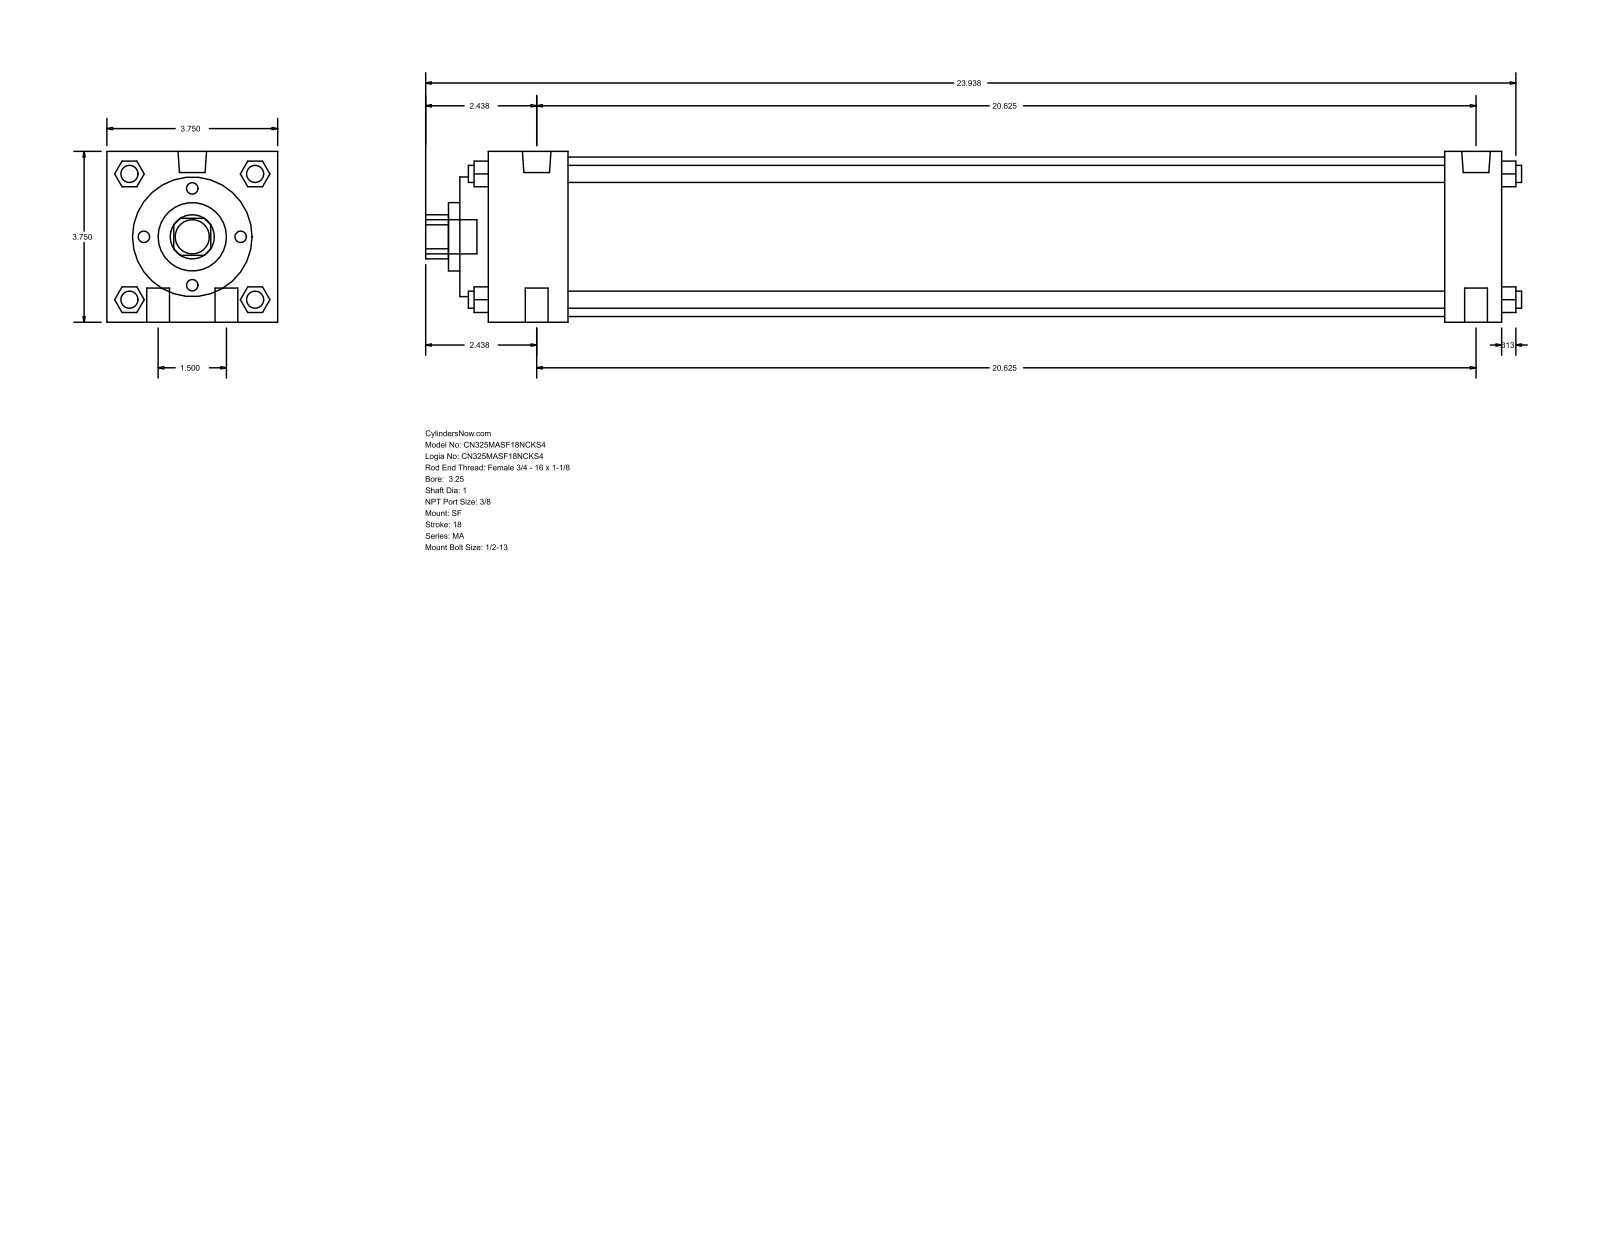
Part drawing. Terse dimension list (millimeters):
name: MA_SF__0325_1
written by: GSSL Pune (CONFIG_CONTROL_DESIGN)
unit: mm
bodies: 0 solids, 126 faces (95 planar, 31 cylindrical, 0 other)
size: 611.19 × 95.25 × 95.25
holes: 1× ⌀25.4, 1× ⌀38.1, 1× ⌀66.67, 1× ⌀88.9
bosses: 4× ⌀12.7, 4× ⌀9.53, 2× ⌀15.93, 2× ⌀11.11, 1× ⌀19.05
rounds: 1× R12.29
face distances: 95.24, 565.16, 15.87, 533.41, 31.75, 44.46, 488.95, 520.7, 60.33, 549.28
